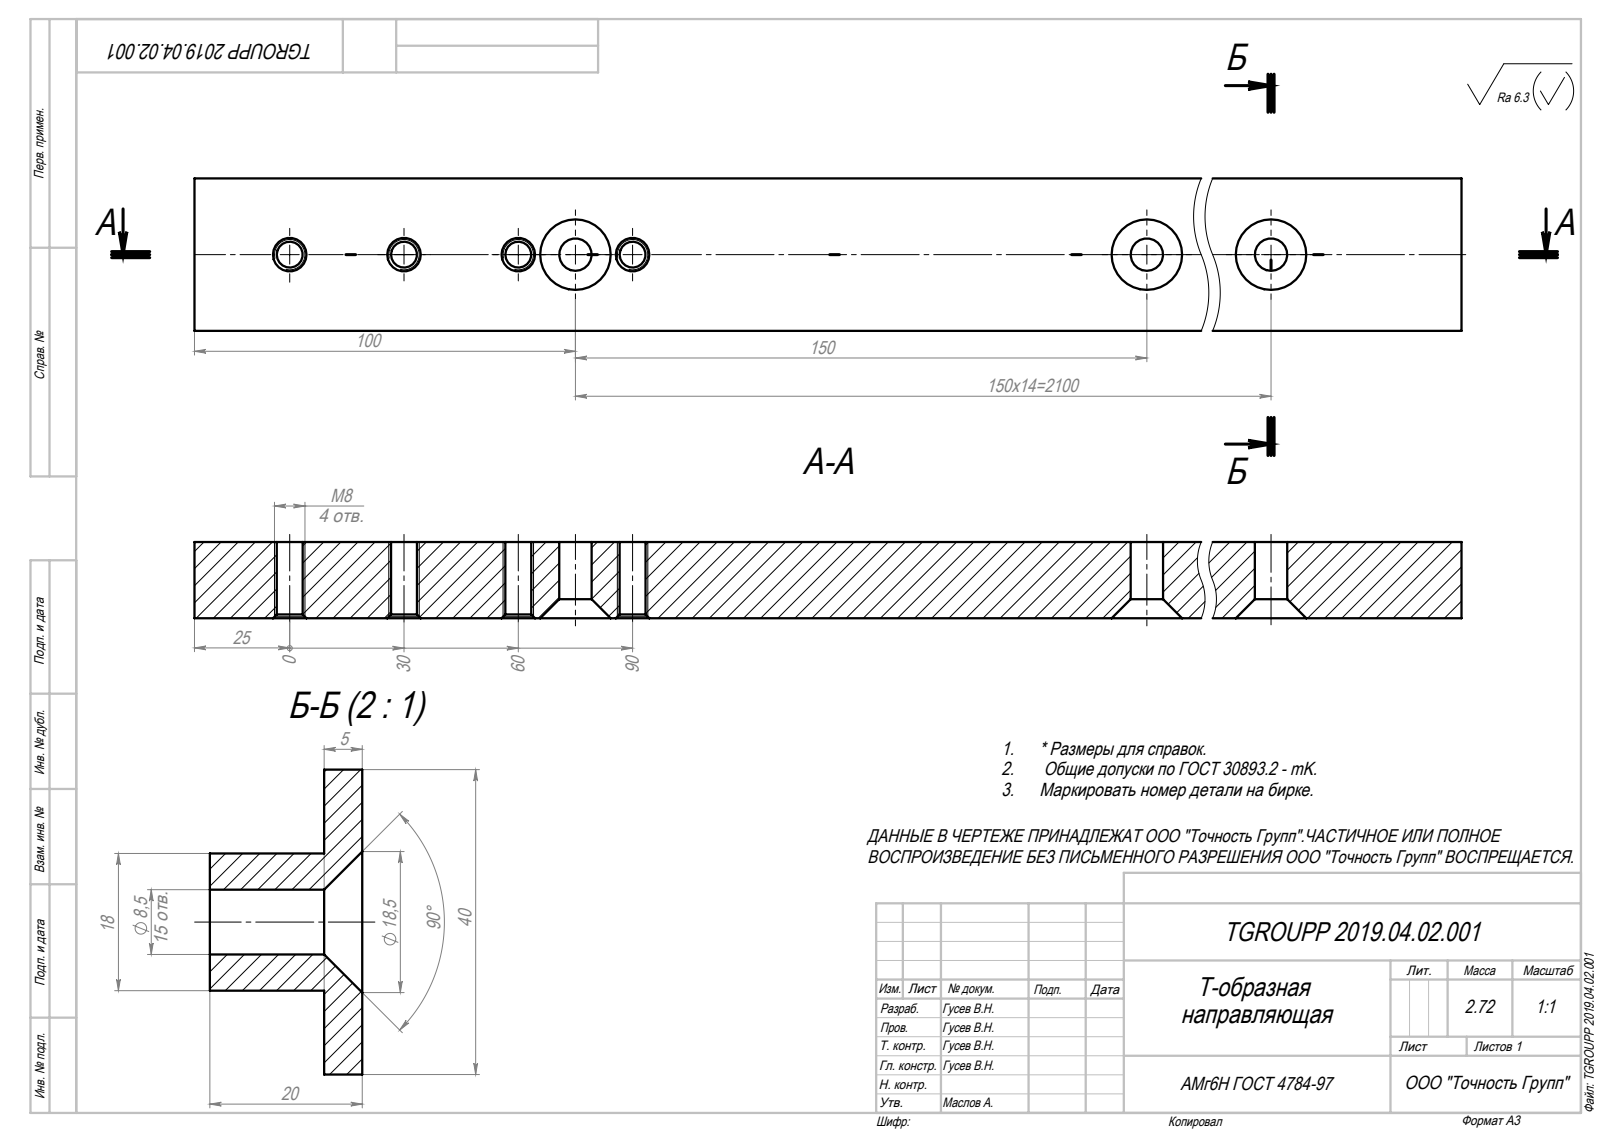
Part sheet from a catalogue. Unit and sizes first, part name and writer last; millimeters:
Units: millimetres
Overall size (bounding box): 2250 × 40 × 20
Round holes (diameter × count): ⌀8.5 ×15, ⌀6.8 ×4
Main face-to-face distances: 5, 20, 15, 18, 11, 29, 40, 2250
Hole centre spacings: 150, 300, 450, 600, 750, 900, 1050, 1200
Volume: 1 031 000 mm³ · Surface area: 277 937 mm²
Bodies: 1 solid, 86 faces (10 planar, 38 cylindrical, 38 other)
Part name (STEP PRODUCT): TGROUPP 2019.04.02.001
STEP written by: SolidWorks 2016 (AUTOMOTIVE_DESIGN)
